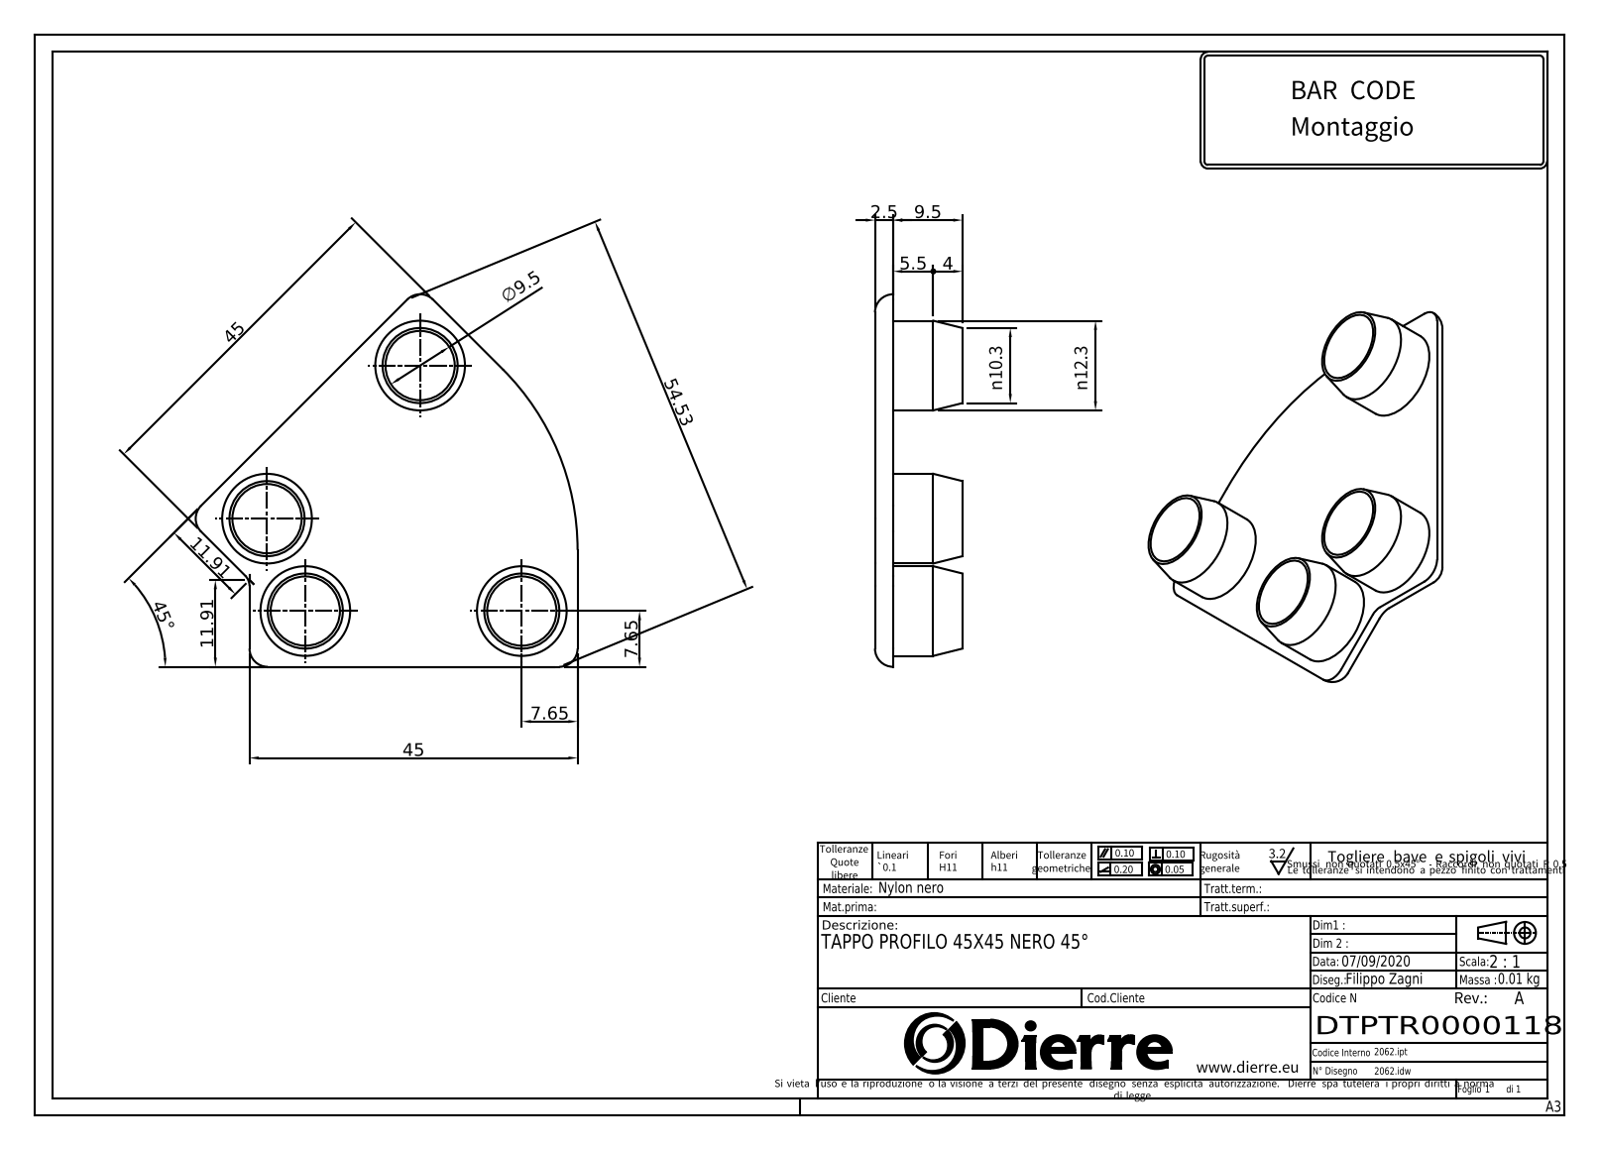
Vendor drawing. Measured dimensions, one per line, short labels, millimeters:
name: 2062
written by: Autodesk Inventor 2019 (AUTOMOTIVE_DESIGN)
unit: mm
bodies: 1 solid, 34 faces (10 planar, 14 cylindrical, 10 other)
size: 52.38 × 51.11 × 12
volume: 6 004 mm³; area: 6 424 mm²
holes: 4× ⌀9.5
bosses: 4× ⌀12.3
rounds: 6× R2.5
face distances: 2.5, 9.5, 12
hole spacings: 29.7, 13.71, 36.45, 37.17, 37.18
